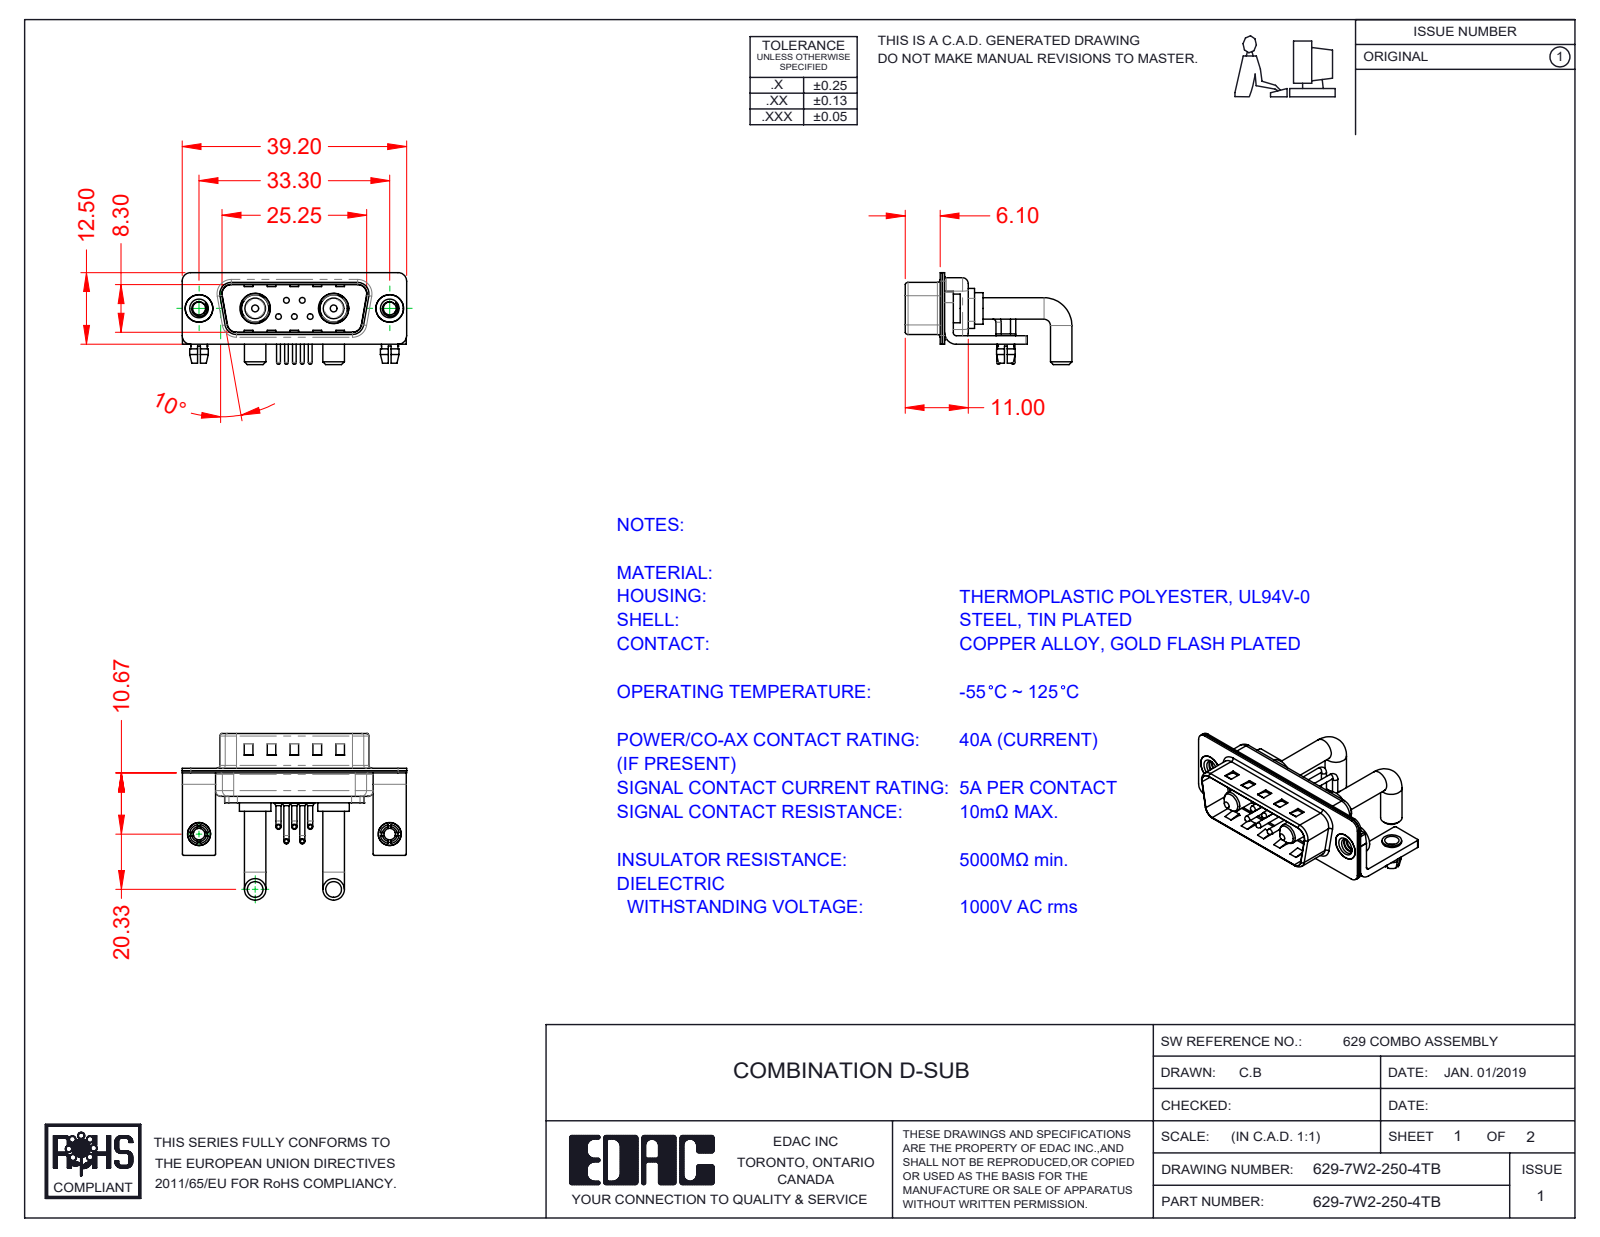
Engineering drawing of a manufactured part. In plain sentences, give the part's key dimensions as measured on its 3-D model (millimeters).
The part is named "629Combo Stabilizer Bracket; Power Pin_Ext 40A RA; 629Combo Threaded Rivet_2; 629Combo Shell Rear_15 Contacts (+6 more)". Its 3-D file was written by "SolidWorks 2020 (CONFIG_CONTROL_DESIGN)". It is 18 solids with 1116 faces: 547 planar, 411 cylindrical and 158 other. Overall it measures 39.2 by 29.11 by 16.05 millimeters. Its volume is 2 806 cubic millimeters and its surface area 6 203 square millimeters. Round holes: 7 of diameter 2, 5 of diameter 0.75, 5 of diameter 1.6, 2 of diameter 2.26, 2 of diameter 2.5, 2 of diameter 3.2, 2 of diameter 4, 2 of diameter 4.8, 2 of diameter 4.85, 2 of diameter 5.3. Round bosses or shafts: 10 of diameter 0.9, 5 of diameter 1.5, 5 of diameter 1, 5 of diameter 0.65, 4 of diameter 3.75, 2 of diameter 5.5, 2 of diameter 5.2, 2 of diameter 5. Partial cylindrical surfaces (rounded edges, fillets, slot ends): 16 of radius 0.25, 16 of radius 1.5, 13 of radius 2, 9 of radius 0.5, 8 of radius 1.6, 5 of radius 1.01, 4 of radius 0.6, 4 of radius 0.65. The main face-to-face distances are 0.4, 0.8, 1.5, 9.5, 9.1, 8.7, 9.9, 0.6, 1.2, 5.2. The hole center spacings are 3.16, 2.77, 9.8, 23.5, 33.3, 4.31, 4.33, 5.03.
